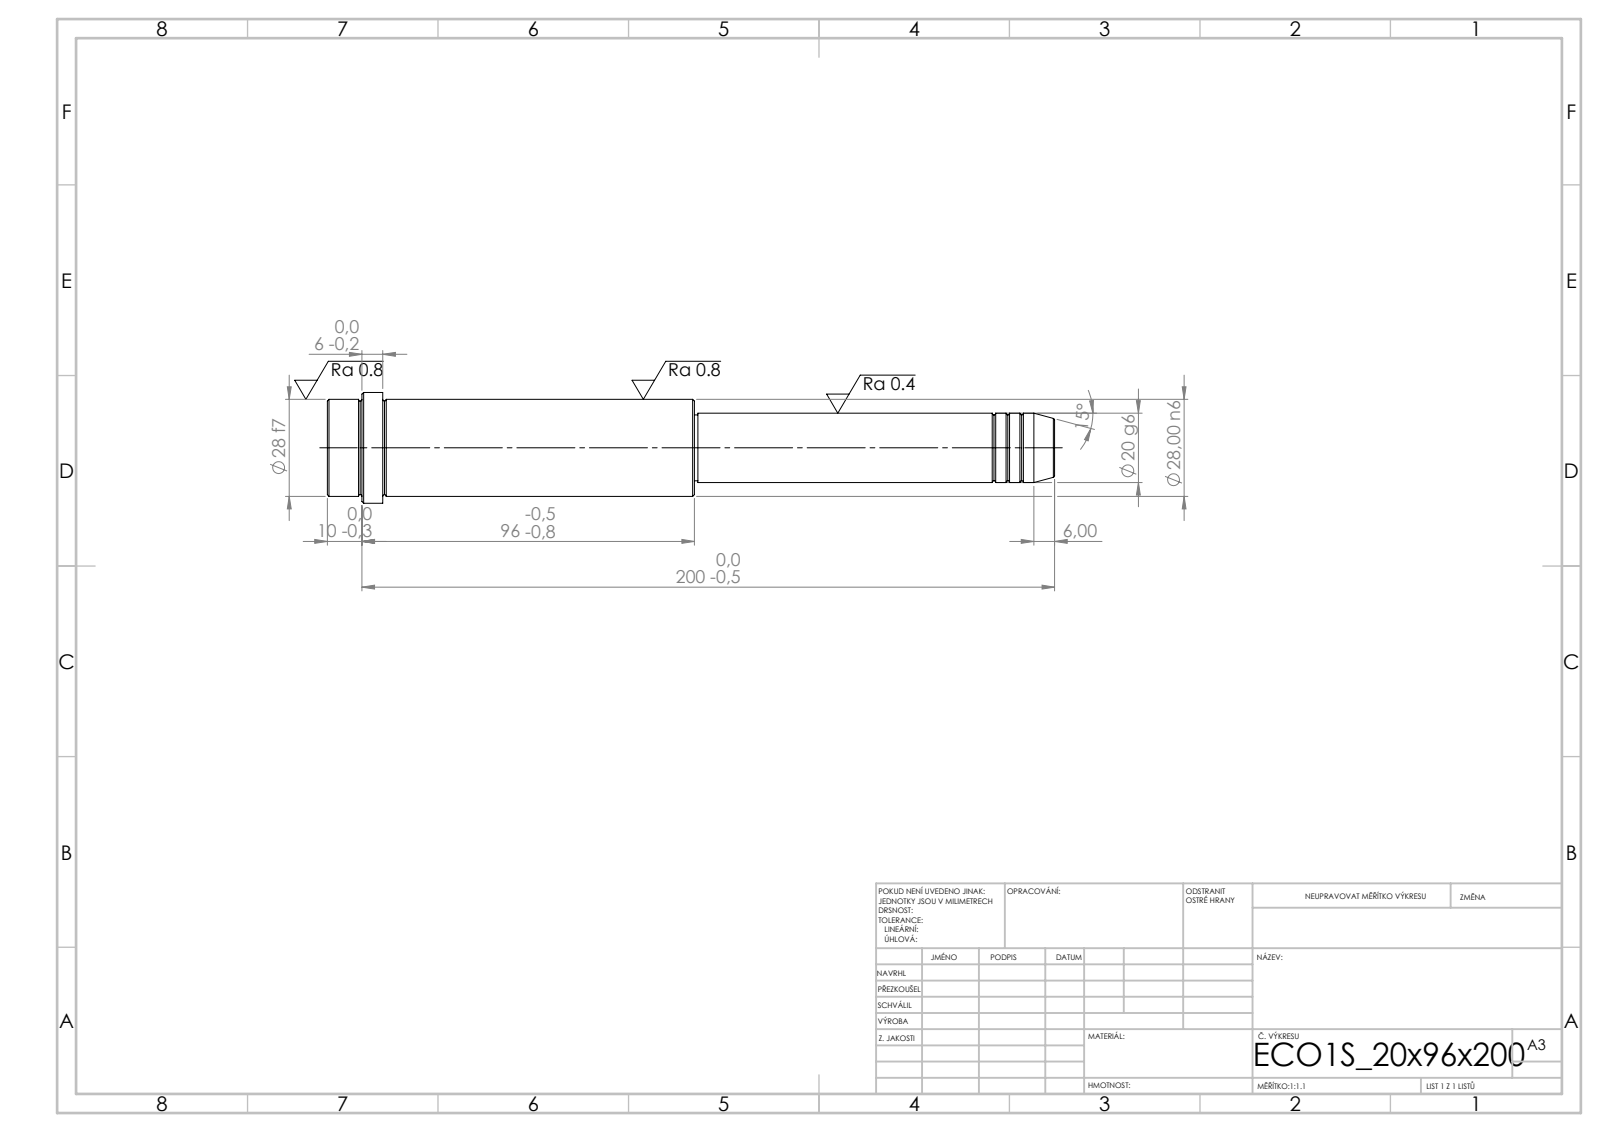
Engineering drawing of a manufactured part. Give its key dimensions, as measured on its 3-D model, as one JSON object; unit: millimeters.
{"step_written_by": "SolidWorks 2019 (CONFIG_CONTROL_DESIGN)", "units": "millimeters", "bodies": {"solids": 1, "faces": 52, "planar": 6, "cylindrical": 16, "other": 30}, "overall_size": [210, 32, 32], "volume_mm3": 98580, "surface_area_mm2": 17594, "round_bosses_or_shafts": [[32, 1], [28, 1], [20, 1], [19, 1]], "face_to_face_distances": [106, 104, 210, 194, 90, 16, 200, 96, 6, 10]}
